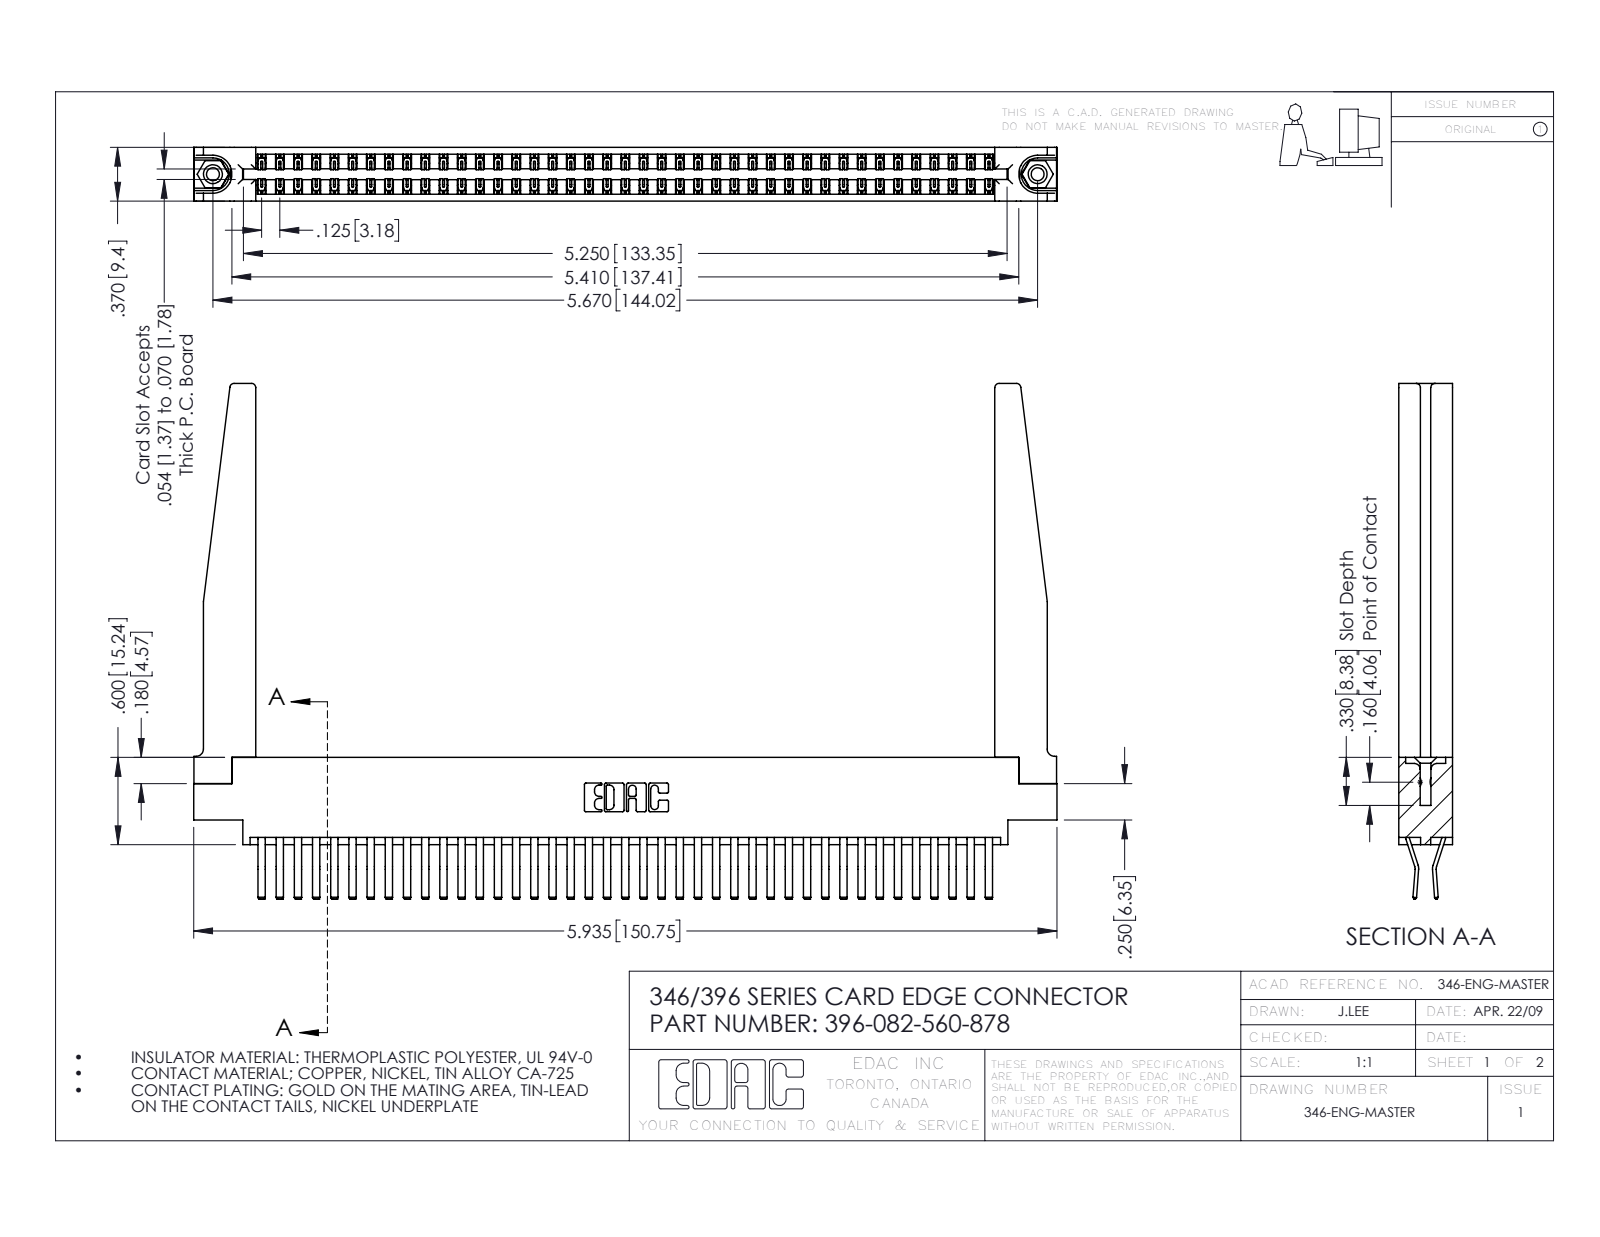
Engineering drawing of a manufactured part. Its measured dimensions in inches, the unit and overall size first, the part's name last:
Units: inches
Overall size (bounding box): 5.935 × 3.545 × 0.37
Round holes (diameter × count): ⌀0.089 ×2, ⌀0.125 ×2, ⌀0.156 ×2, ⌀0.064 ×1
Round bosses / shafts (diameter × count): ⌀0.155 ×2
Partial cylindrical surfaces — rounded edges, fillets, slot ends (radius × count): R0.006 ×123, R0.01 ×22, R0.03 ×8, R0.007 ×6, R0.031 ×6, R0.05 ×4, R0.026 ×3, R0.01 ×2
Main face-to-face distances: 0.37, 0.048, 0.322, 0.072, 0.025, 0.15, 0.148, 0.25, 0.298, 0.275
Hole centre spacings: 0.246, 5.461, 5.67
Volume: 1.342 in³ · Surface area: 44.73 in²
Bodies: 87 solids, 4788 faces (3092 planar, 1644 cylindrical, 52 other)
Part name (STEP PRODUCT): 346 Part_0.170 Offset - 0.156 Dia-TH; 346-220-078_345-220-078; 396-082-560-878; 345-292-001_560 Tail (+1 more)
STEP written by: SolidWorks 2016 (CONFIG_CONTROL_DESIGN)
